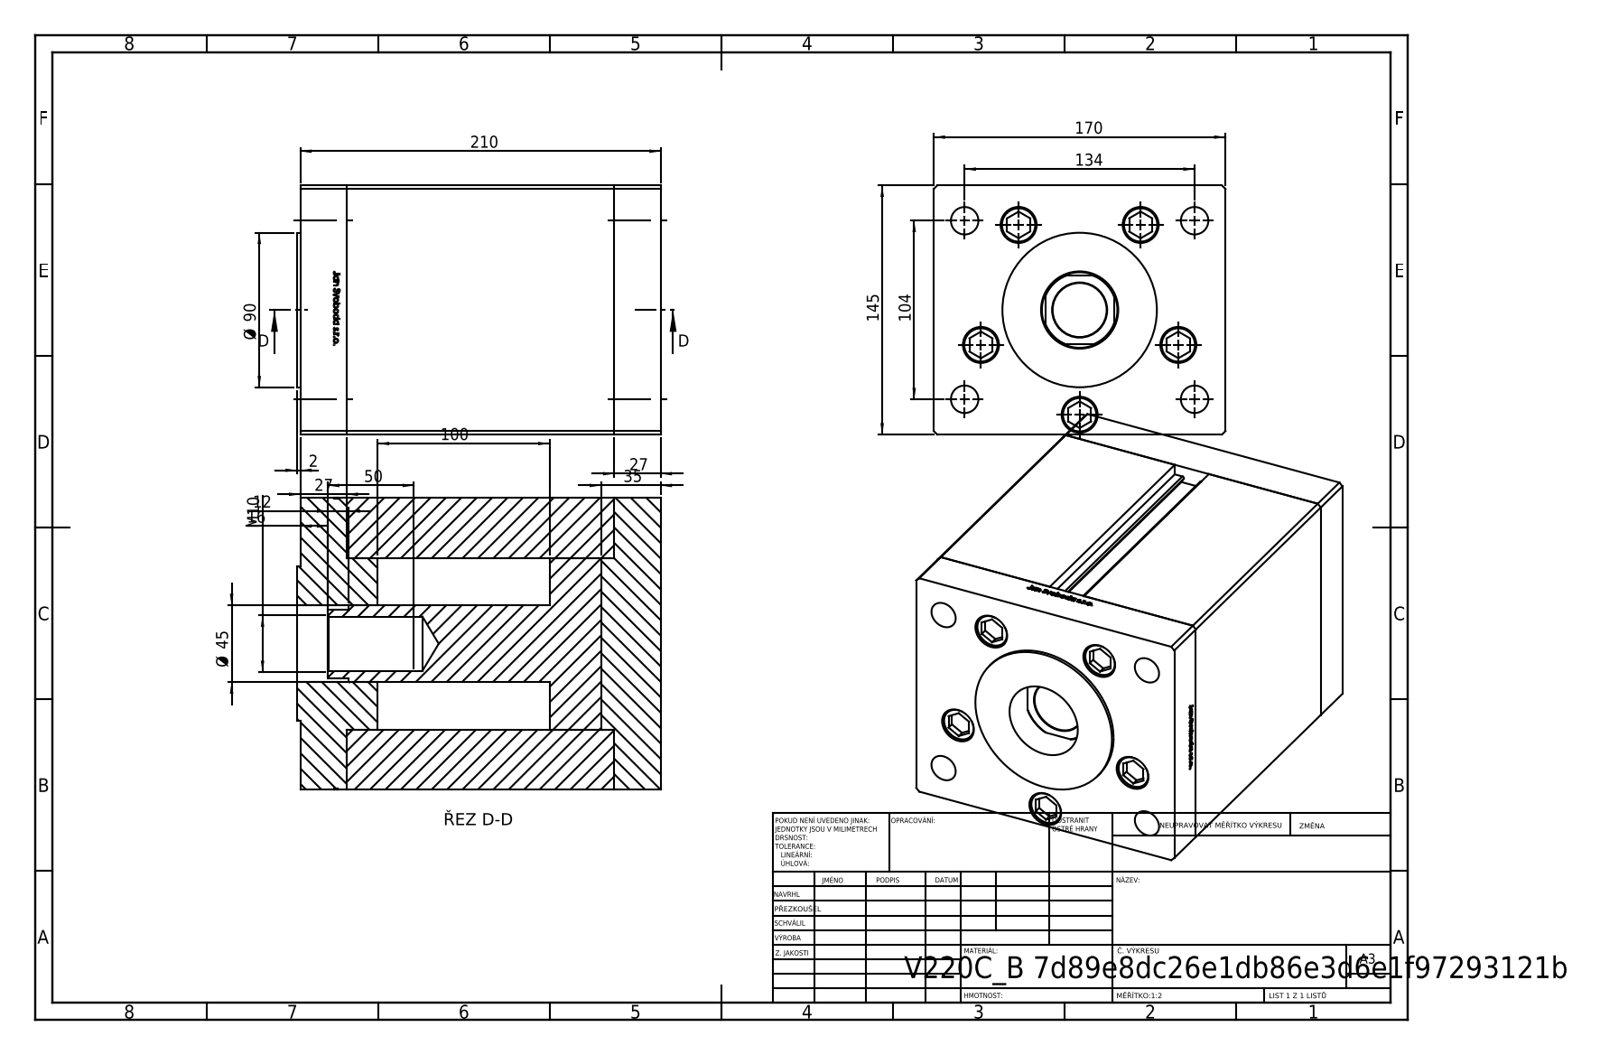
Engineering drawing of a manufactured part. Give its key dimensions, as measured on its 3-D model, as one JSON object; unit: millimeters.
{"part_name": "V220C_B MIDDLE; V220C_FRONT_B; V220C BACK_B; V220C_VC_B (+1 more)", "step_written_by": "SolidWorks 2019 (CONFIG_CONTROL_DESIGN)", "units": "millimeters", "bodies": {"solids": 14, "faces": 1185, "planar": 464, "cylindrical": 147, "other": 574}, "overall_size": [212, 170, 145], "volume_mm3": 4330000, "surface_area_mm2": 421836, "round_holes": [[17.5, 5], [21, 5], [16, 4], [2, 2], [13.16, 2], [31.5, 1], [45, 1]], "round_bosses_or_shafts": [[8, 5], [100, 1], [90, 1]], "partial_cylinders_radius": [[0.93, 2], [22, 1]], "face_to_face_distances": [27, 183, 145, 156, 170, 7.8, 210, 34.8, 148.2, 175.2], "hole_center_spacings": [61, 84.81, 31.53, 33.06, 67.6, 70.44, 72.95, 73.26]}
